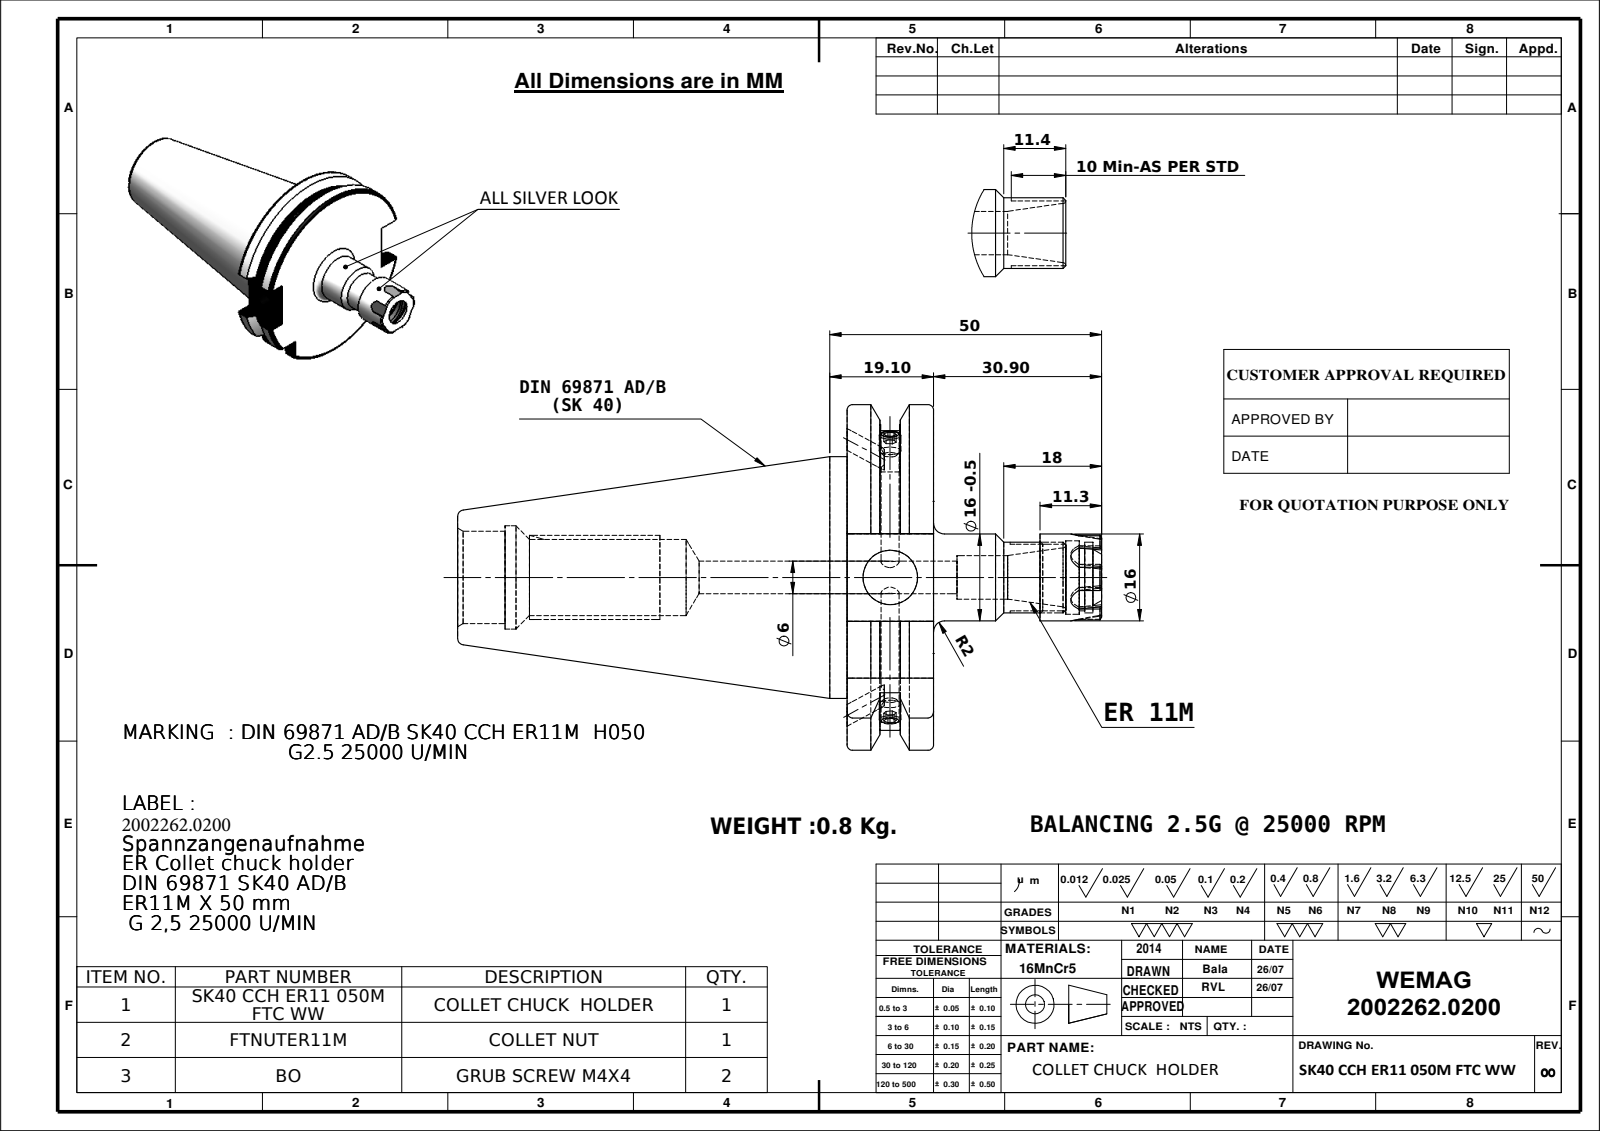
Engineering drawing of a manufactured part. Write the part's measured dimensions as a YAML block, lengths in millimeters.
part_name: "SK40 CCH ER11 050M FTC WW; M4X4_DIN 913 - M4 x 4-N; FTNUTER11M"
step_written_by: "SolidWorks 2009 (CONFIG_CONTROL_DESIGN)"
units: millimeters
bodies: {solids: 4, faces: 179, planar: 70, cylindrical: 48, other: 61}
overall_size: [118.4, 63.55, 61.48]
volume: 107337
surface_area: 23481
round_holes:
  - {diameter: 3.3, count: 1}
  - {diameter: 6, count: 1}
  - {diameter: 8, count: 1}
  - {diameter: 10, count: 1}
  - {diameter: 11.5, count: 1}
  - {diameter: 12.25, count: 1}
  - {diameter: 13, count: 1}
  - {diameter: 13.5, count: 1}
  - {diameter: 14, count: 1}
  - {diameter: 17, count: 1}
  - {diameter: 19, count: 1}
round_bosses_or_shafts:
  - {diameter: 4, count: 2}
  - {diameter: 44.45, count: 1}
  - {diameter: 16, count: 1}
partial_cylinders:
  - {radius: 28.12, count: 1}
  - {radius: 31.77, count: 1}
face_to_face_distances: [15.9, 16.1, 47.8, 87.5, 71.6, 30.9, 46.8, 118.4, 40.77, 9.87]
hole_center_spacings: [0.75]
